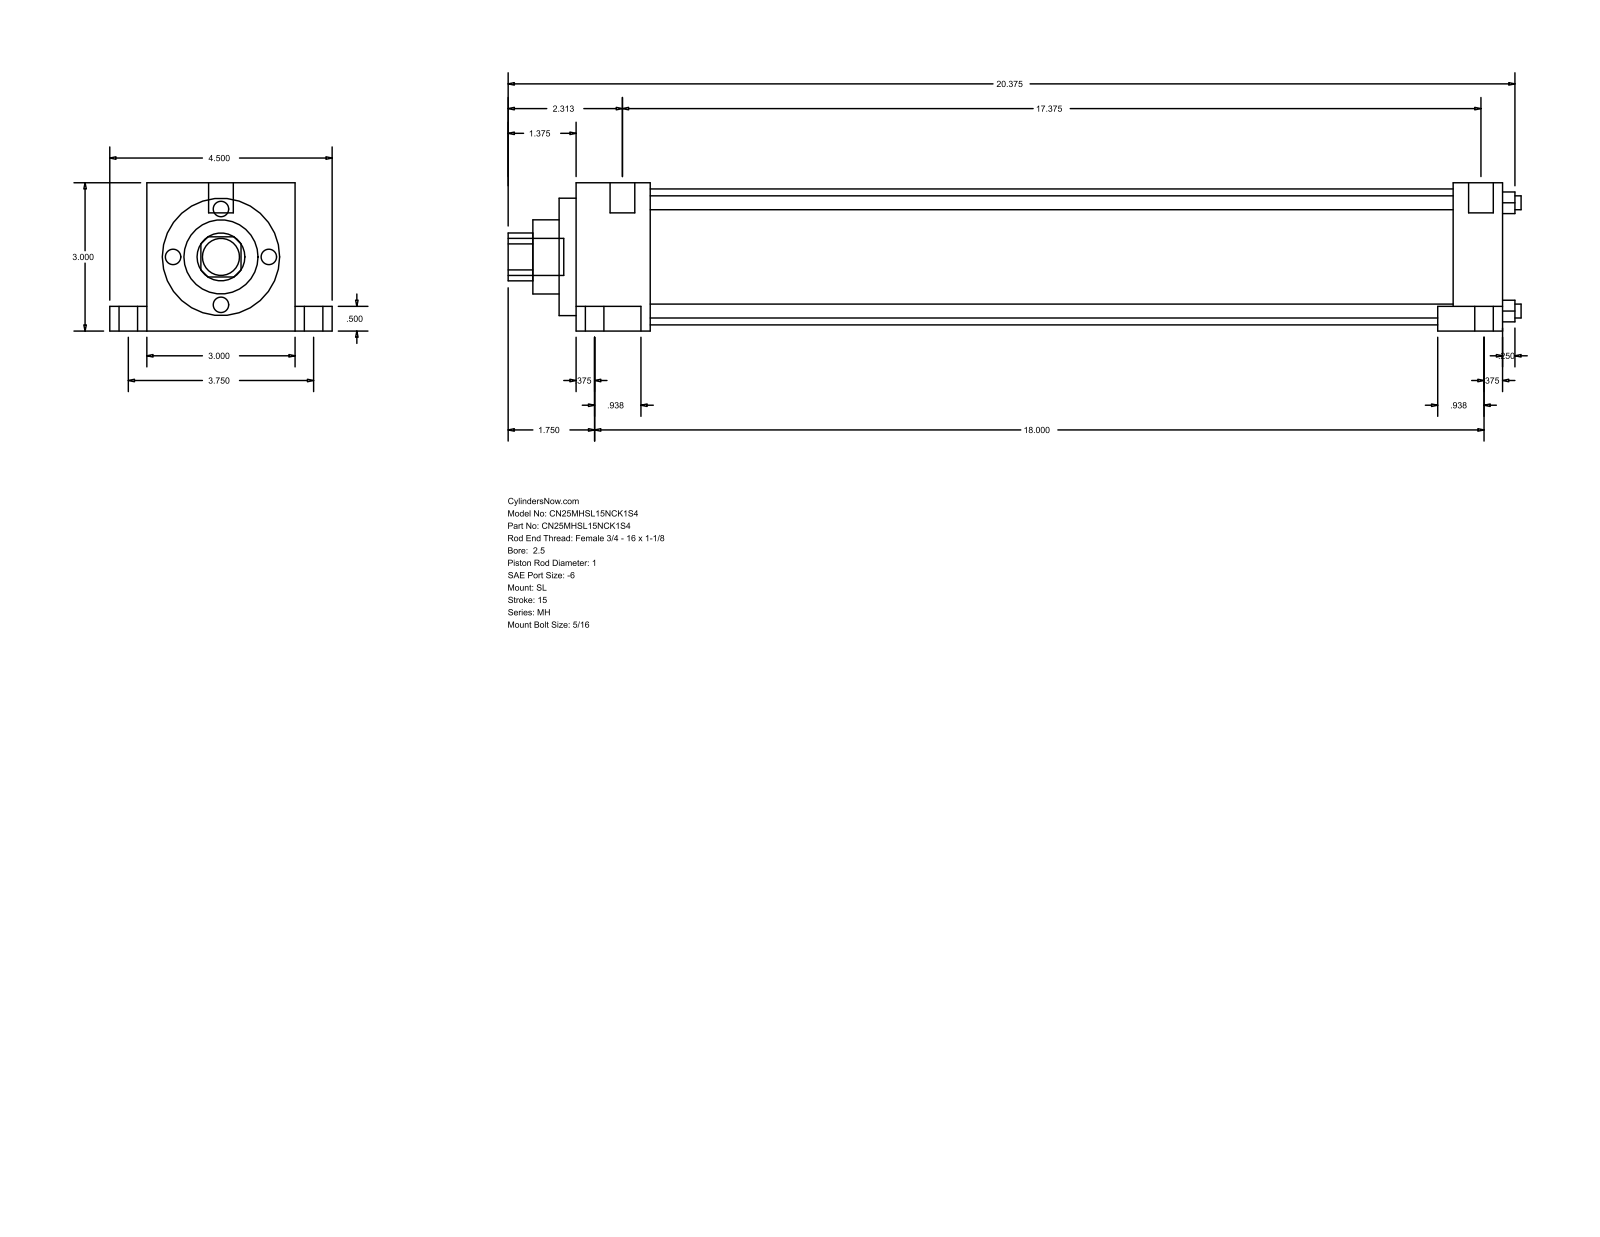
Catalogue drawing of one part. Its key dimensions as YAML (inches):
part_name: "MH_SL__0250_1"
step_written_by: "GSSL Pune (CONFIG_CONTROL_DESIGN)"
units: inches
bodies: {solids: 0, faces: 86, planar: 61, cylindrical: 25, other: 0}
overall_size: [20.5, 4.5, 3]
round_holes:
  - {diameter: 0.281, count: 4}
  - {diameter: 1, count: 1}
  - {diameter: 1.5, count: 1}
  - {diameter: 2.375, count: 1}
  - {diameter: 2.75, count: 1}
round_bosses_or_shafts:
  - {diameter: 0.625, count: 2}
  - {diameter: 0.375, count: 2}
  - {diameter: 0.219, count: 2}
  - {diameter: 0.75, count: 1}
  - {diameter: 0.5, count: 1}
partial_cylinders:
  - {radius: 0.484, count: 1}
face_to_face_distances: [3, 1, 18.094, 19.094, 0.5, 2.5, 0.75, 3.75, 0.531, 18.625]
hole_center_spacings: [1.548, 2.19, 3.097]
